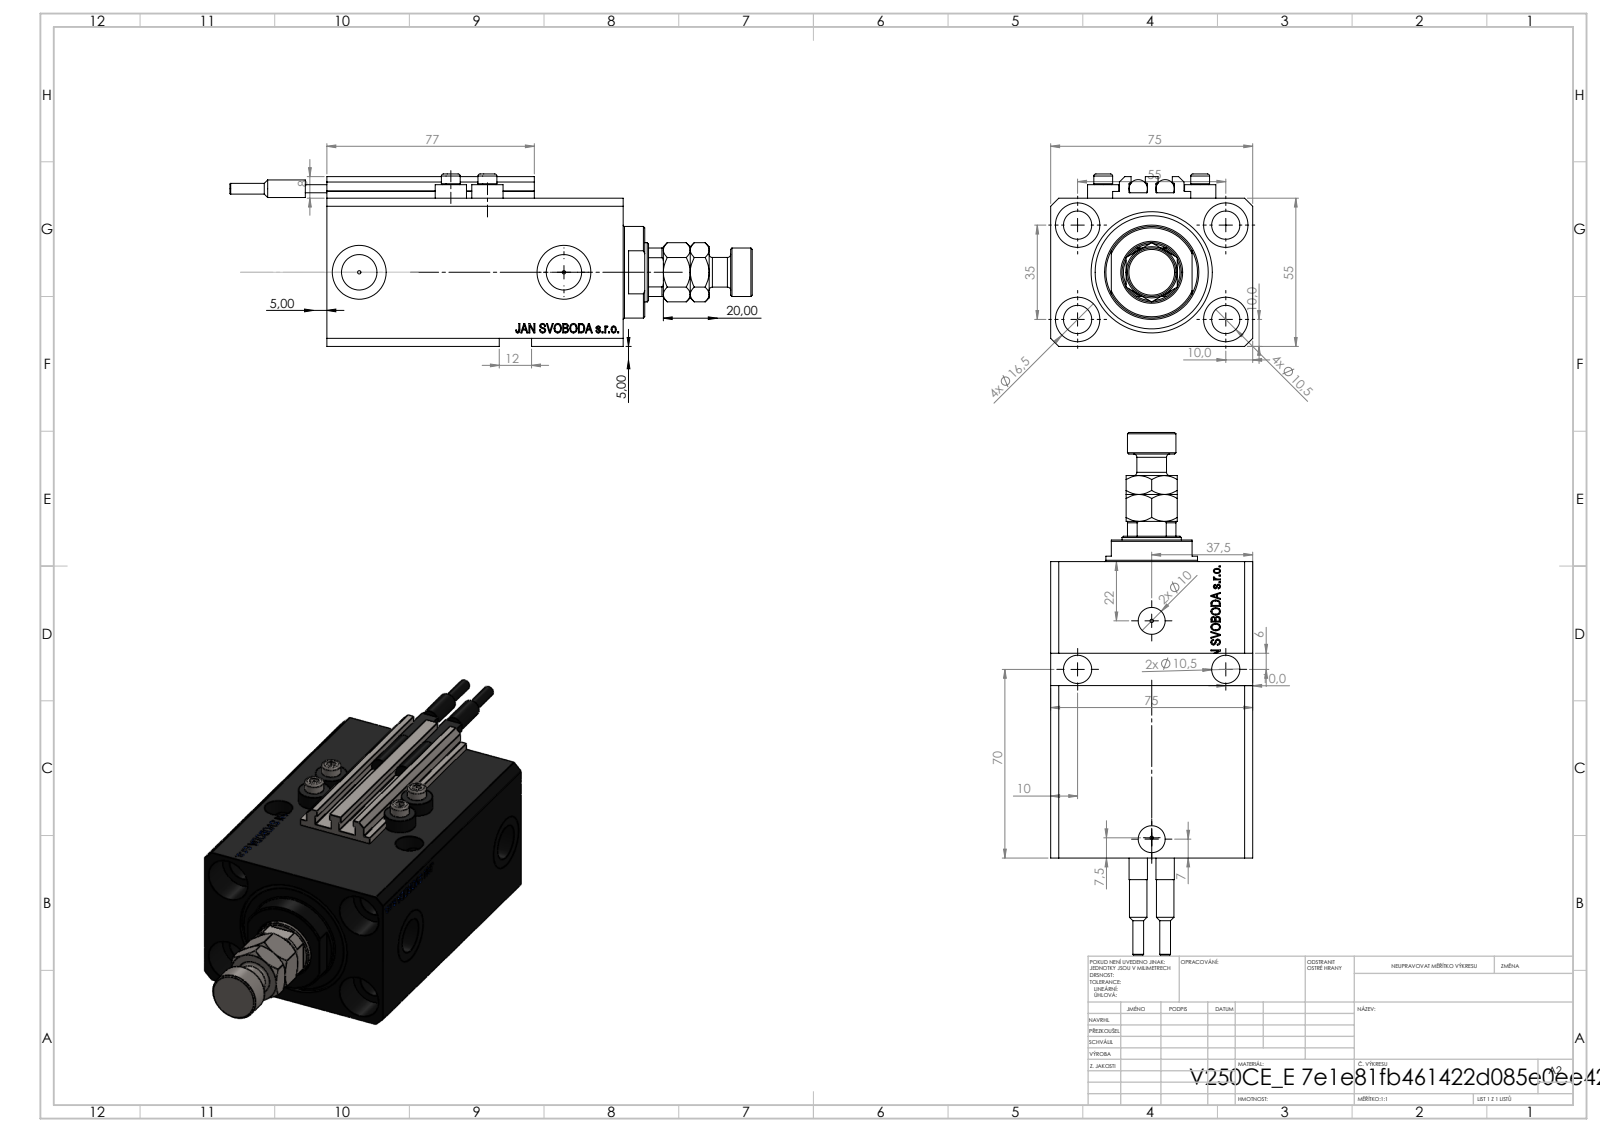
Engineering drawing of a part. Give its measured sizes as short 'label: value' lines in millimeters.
name: ALLEN BOLT V250CE; V250CE_E_Body; SWITCH_V250CE; MFA (+2 more)
written by: SolidWorks 2019 (CONFIG_CONTROL_DESIGN)
unit: mm
bodies: 11 solids, 1204 faces (566 planar, 174 cylindrical, 464 other)
size: 194 × 75 × 64
volume: 389 358 mm³; area: 102 238 mm²
holes: 9× ⌀10.5, 4× ⌀1.25, 4× ⌀4, 4× ⌀16.5, 2× ⌀10, 2× ⌀13.16, 2× ⌀20, 1× ⌀22, 1× ⌀32, 1× ⌀45
bosses: 4× ⌀11.6, 4× ⌀7, 2× ⌀6.8, 2× ⌀6.5, 2× ⌀4, 1× ⌀34, 1× ⌀18, 1× ⌀11
rounds: 10× R0.2, 1× R10.5
face distances: 55, 75, 15, 3, 110, 57, 95, 9.9, 85.1, 100.1
hole spacings: 32.6, 32.87, 55, 68.74, 13.6, 14.09, 23.05, 25.81
